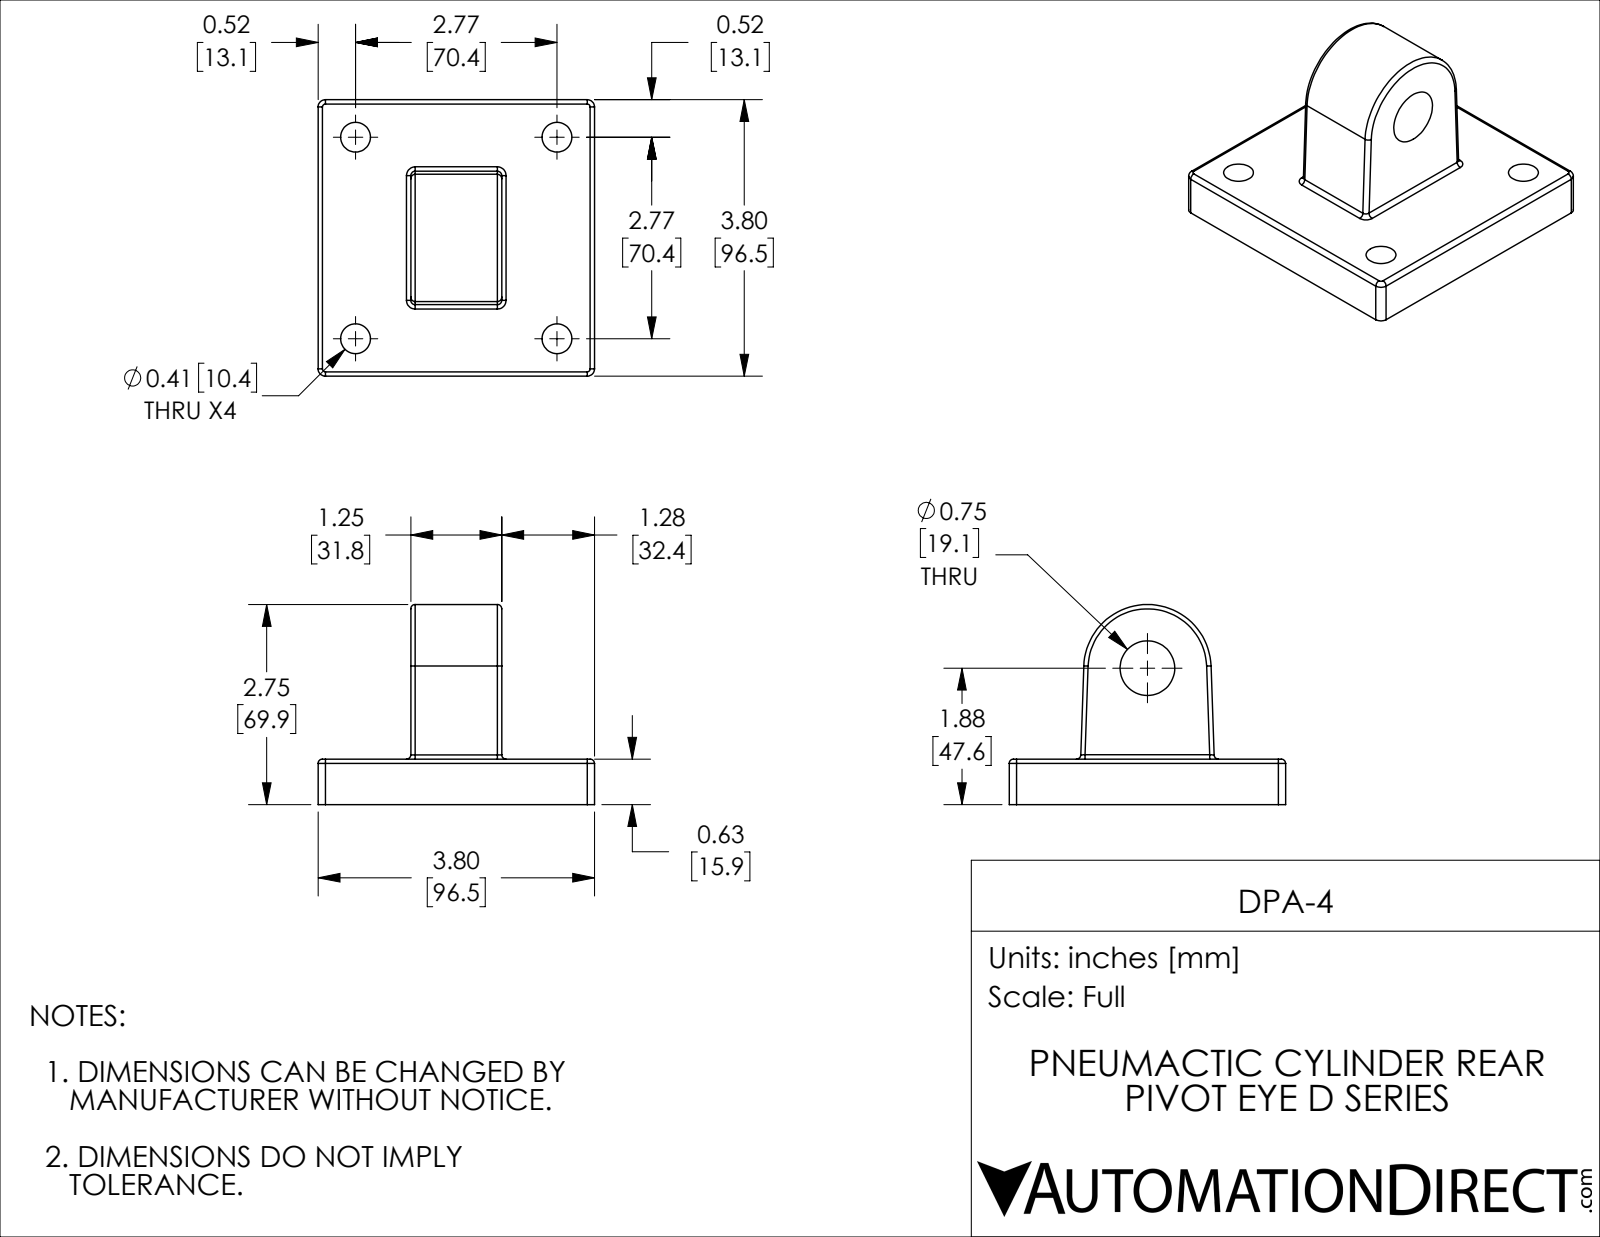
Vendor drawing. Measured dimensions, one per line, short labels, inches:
name: DPA-4
written by: SolidWorks 2018 (AUTOMOTIVE_DESIGN)
unit: in
bodies: 1 solid, 48 faces (10 planar, 28 cylindrical, 10 other)
size: 3.8 × 3.8 × 2.75
volume: 12.43 in³; area: 52.83 in²
holes: 4× ⌀0.41, 1× ⌀0.752
rounds: 12× R0.06, 4× R0.1, 1× R0.875
face distances: 0.625, 1.275, 2.525, 3.8, 1.25
hole spacings: 2.77, 3.917
